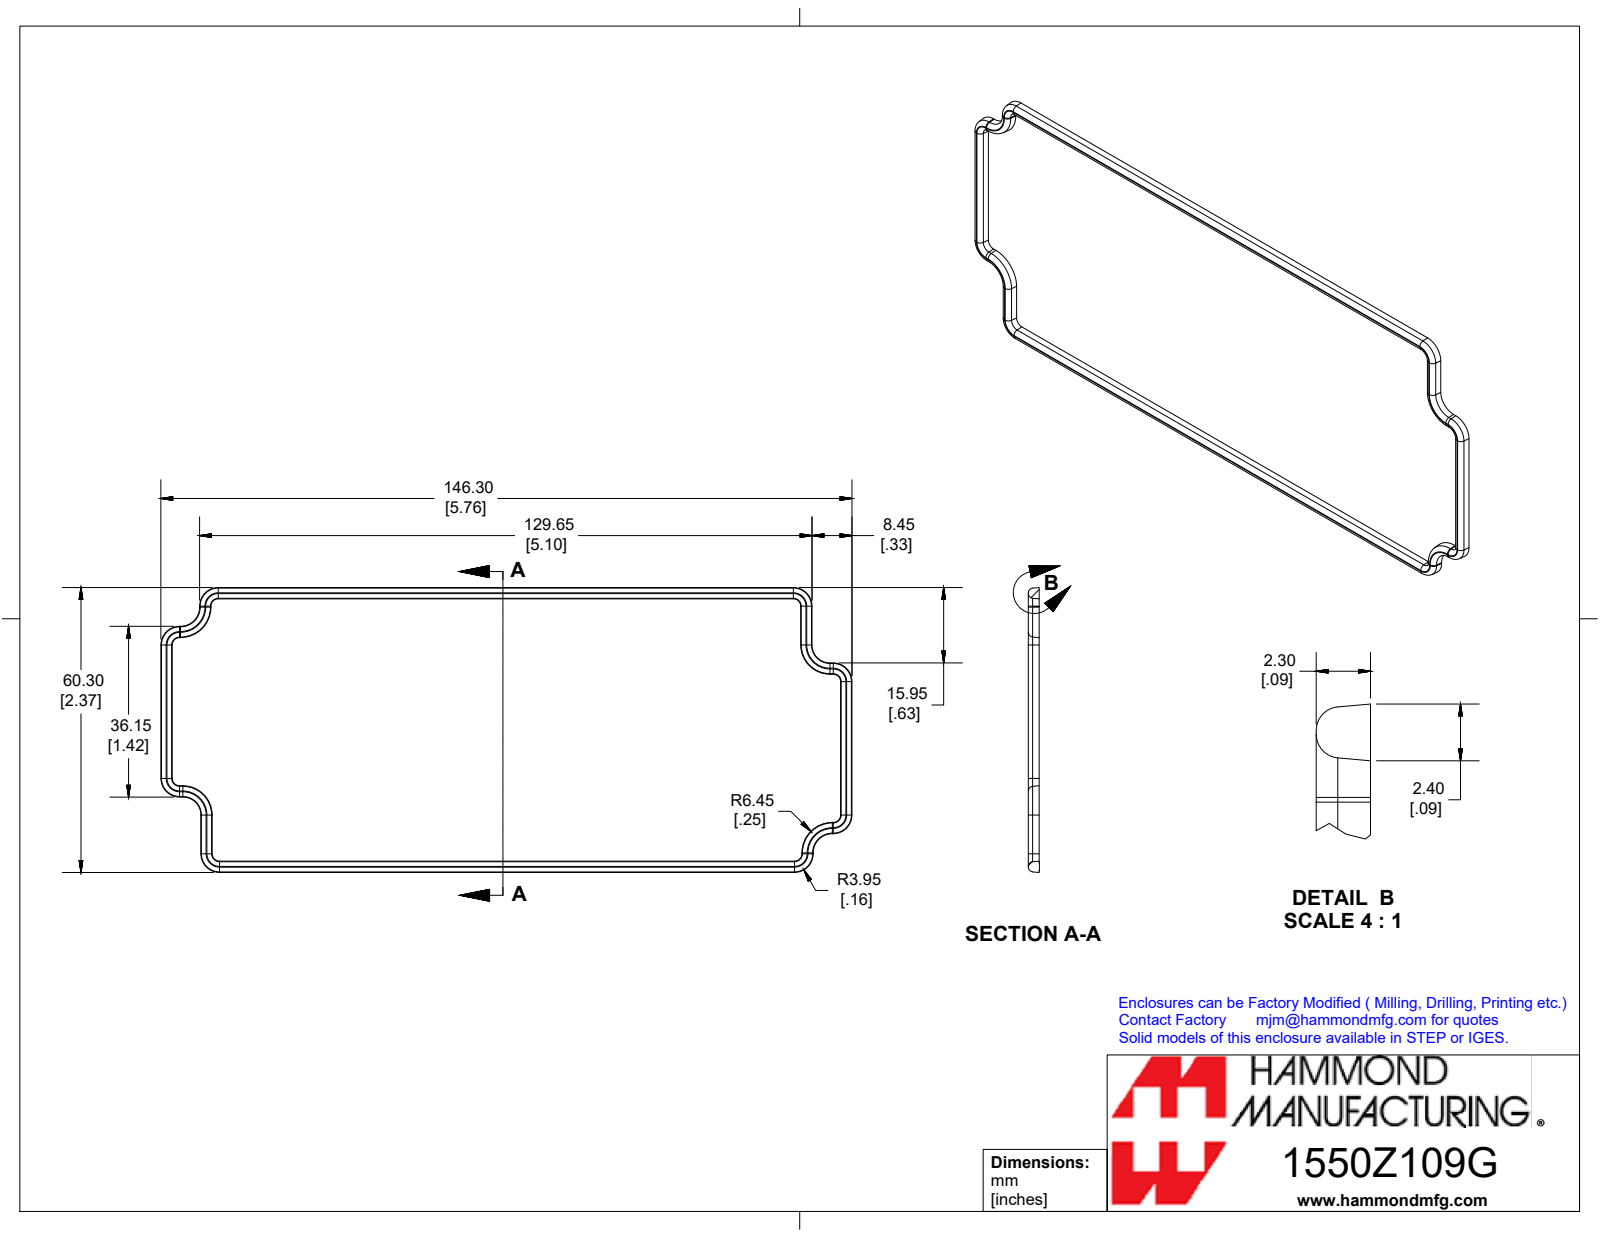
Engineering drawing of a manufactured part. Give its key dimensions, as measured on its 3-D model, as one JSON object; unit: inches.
{"part_name": "1550Z109GASKET", "step_written_by": "SolidWorks 2019 (CONFIG_CONTROL_DESIGN)", "units": "inches", "bodies": {"solids": 1, "faces": 154, "planar": 40, "cylindrical": 24, "other": 90}, "overall_size": [5.76, 2.374, 0.093], "volume_in3": 0.111, "surface_area_in2": 4.97, "partial_cylinders_radius": [[0.039, 24]], "face_to_face_distances": [2.27, 5.643, 0.091, 0.331, 5.311, 4.98, 0.093, 0.626, 1.645, 0.322]}
